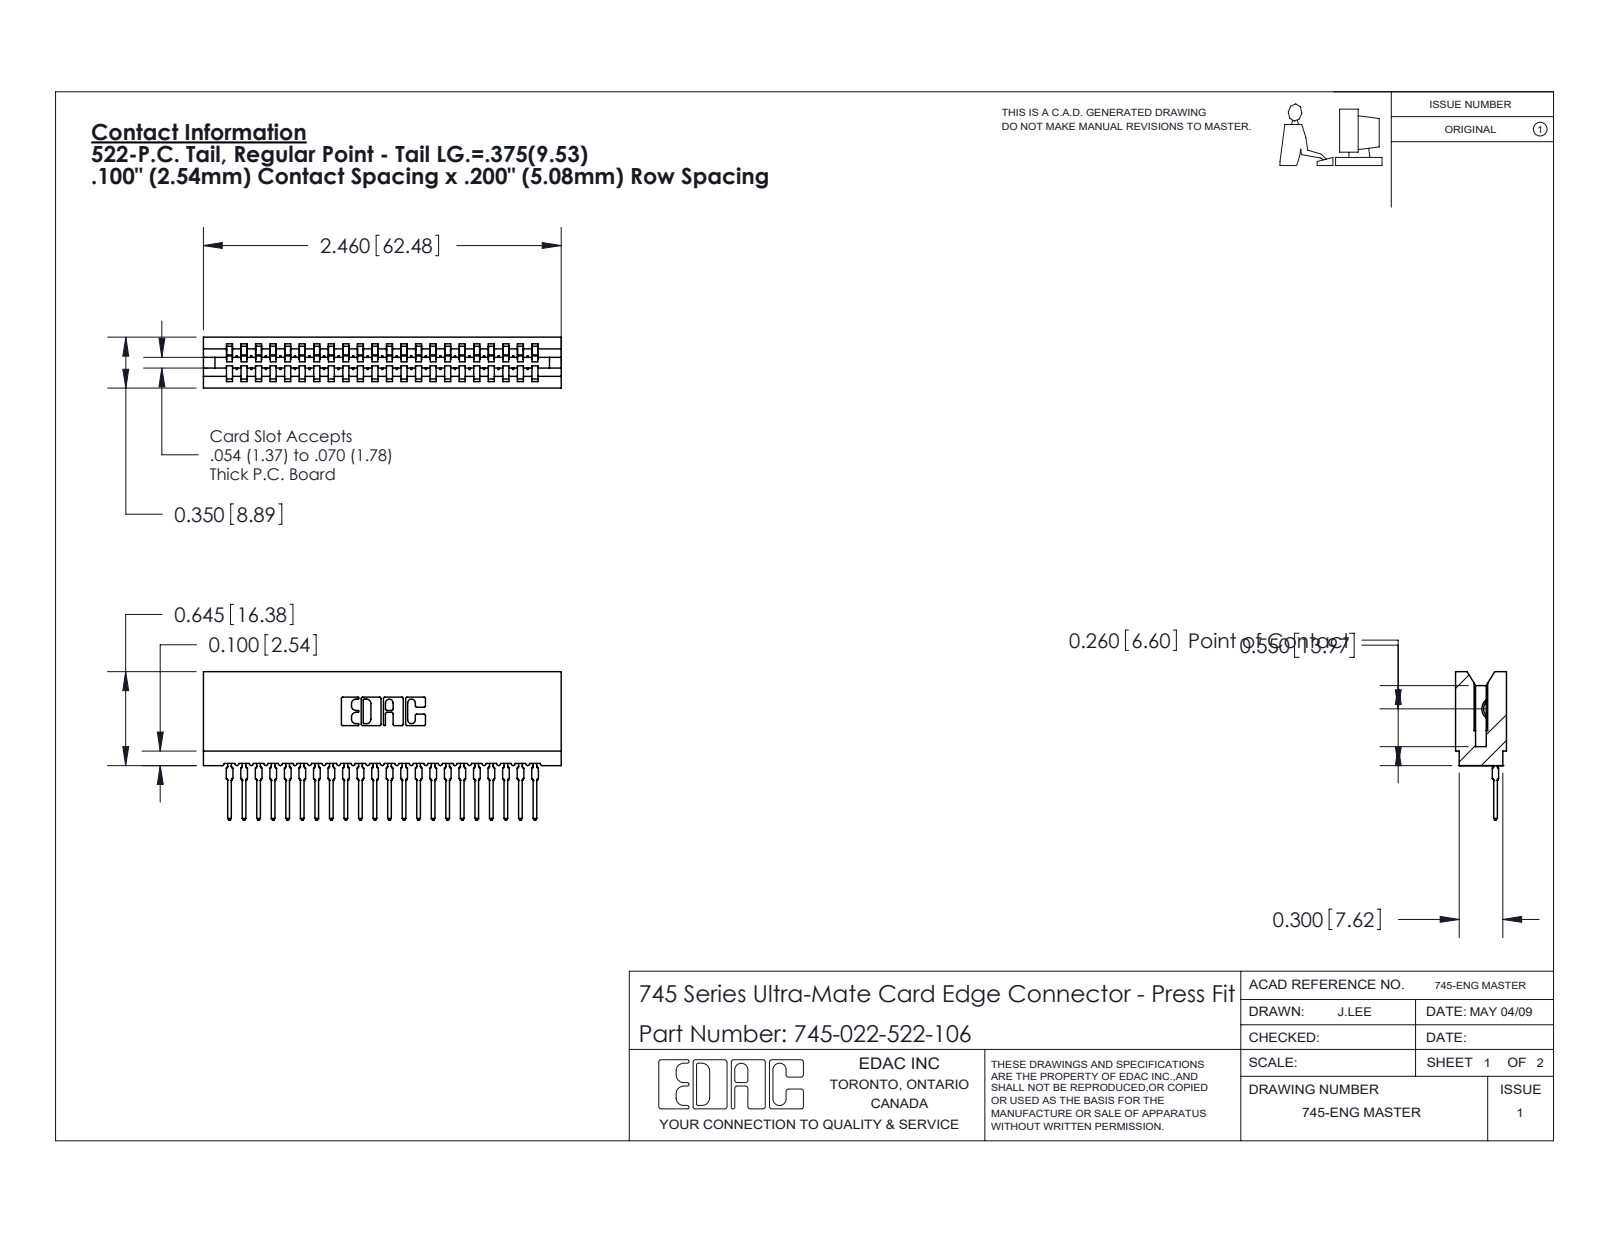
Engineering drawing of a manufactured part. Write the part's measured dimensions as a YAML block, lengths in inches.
part_name: "745-292-001_522; 745-022-522-106; 745 Part_Insulator Option - 06"
step_written_by: "SolidWorks 2020 (CONFIG_CONTROL_DESIGN)"
units: inches
bodies: {solids: 23, faces: 2560, planar: 1530, cylindrical: 458, other: 572}
overall_size: [2.46, 1.021, 0.35]
volume: 0.338
surface_area: 15.49
partial_cylinders:
  - {radius: 0.015, count: 44}
  - {radius: 0.021, count: 44}
  - {radius: 0.01, count: 22}
  - {radius: 0.007, count: 6}
  - {radius: 0.031, count: 6}
  - {radius: 0.005, count: 4}
  - {radius: 0.011, count: 4}
  - {radius: 0.026, count: 3}
face_to_face_distances: [0.2, 0.1, 0.3, 0.4, 0.35, 0.5, 0.6, 0.138, 0.212, 0.7]
